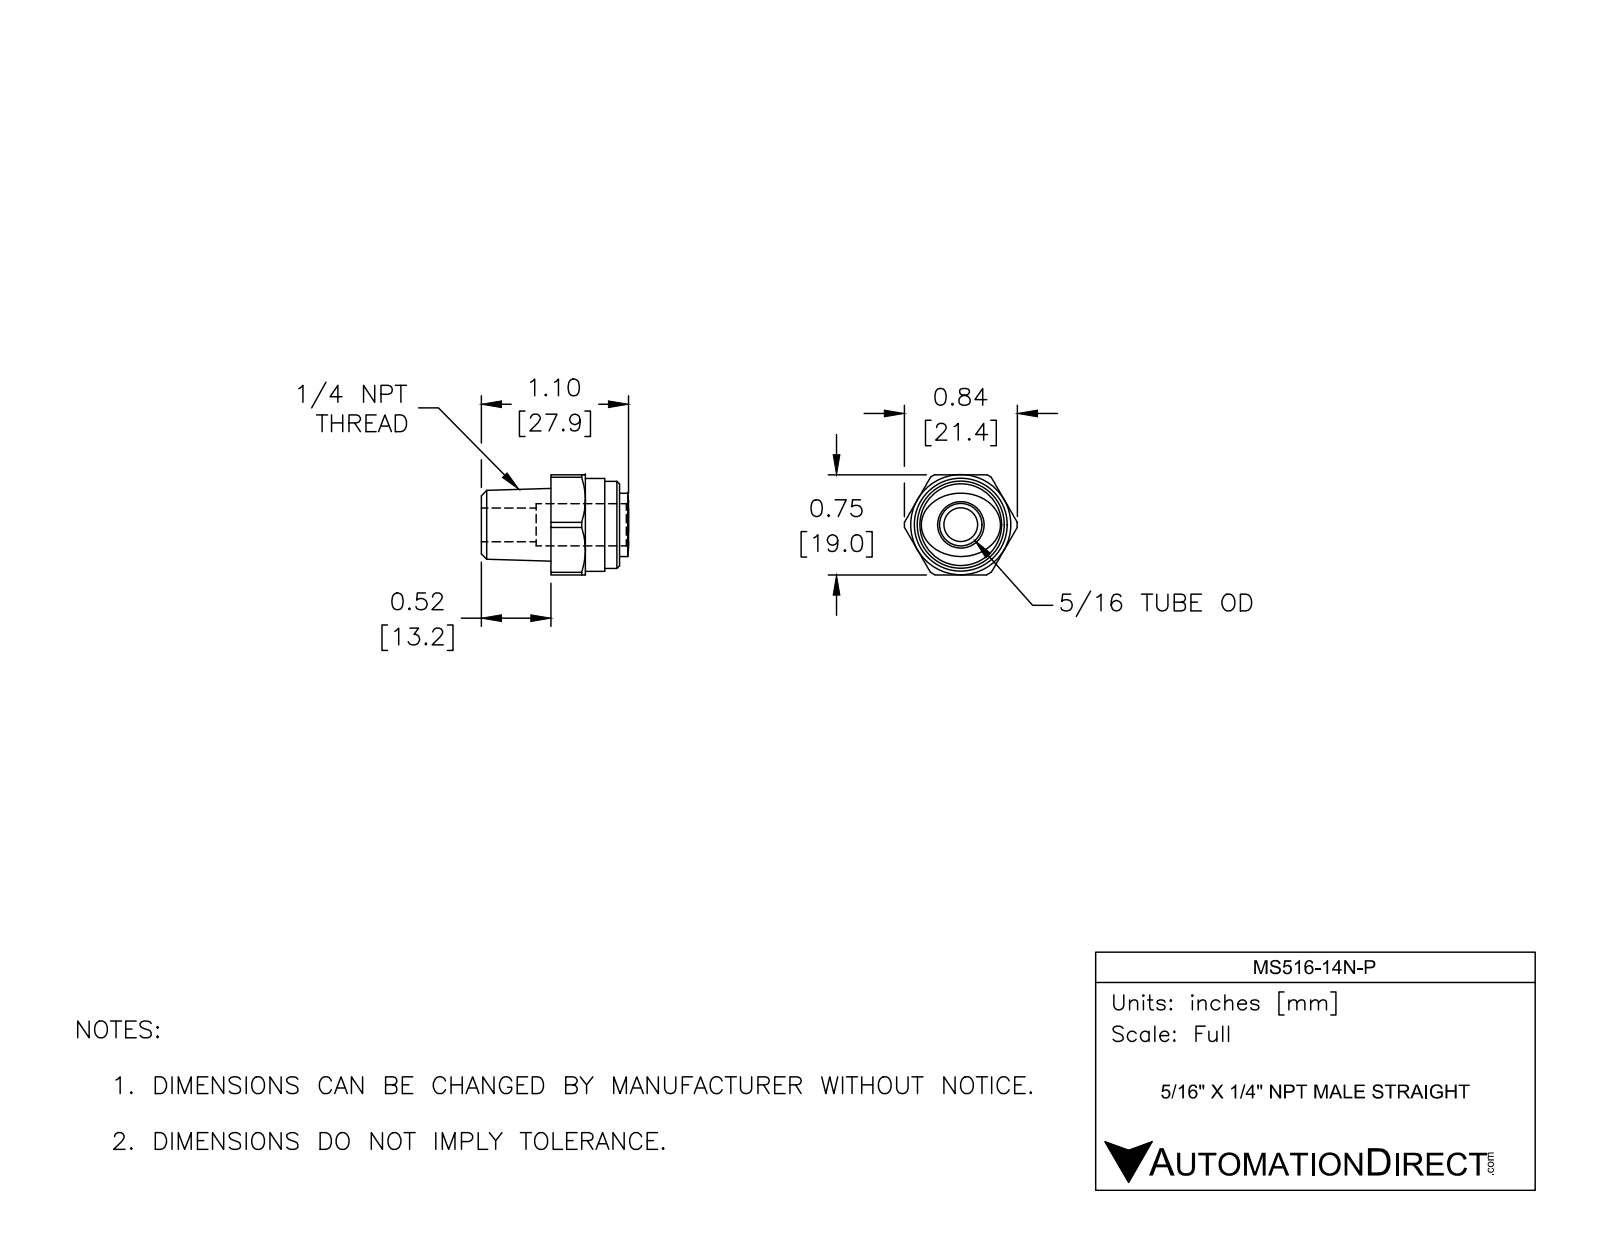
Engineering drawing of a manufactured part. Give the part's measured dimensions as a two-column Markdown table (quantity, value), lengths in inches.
| quantity | value |
| --- | --- |
| part name | MS516-14N-P |
| STEP written by | SolidWorks 2017 (AUTOMOTIVE_DESIGN) |
| units | inches |
| bodies | 1 solid, 44 faces (12 planar, 14 cylindrical, 18 other) |
| overall size | 1.098 × 0.843 × 0.748 |
| volume | 0.267 in³ |
| surface area | 3.915 in² |
| round holes (diameter × count) | 0.252 × 1, 0.315 × 1 |
| round bosses / shafts (diameter × count) | 0.693 × 1, 0.65 × 1 |
| partial cylindrical surfaces (radius × count) | 0.421 × 1 |
| main face-to-face distances | 0.748, 0.256, 0.512, 0.52, 0.11, 1.031, 0.776, 0.921, 0.402, 0.146 |
